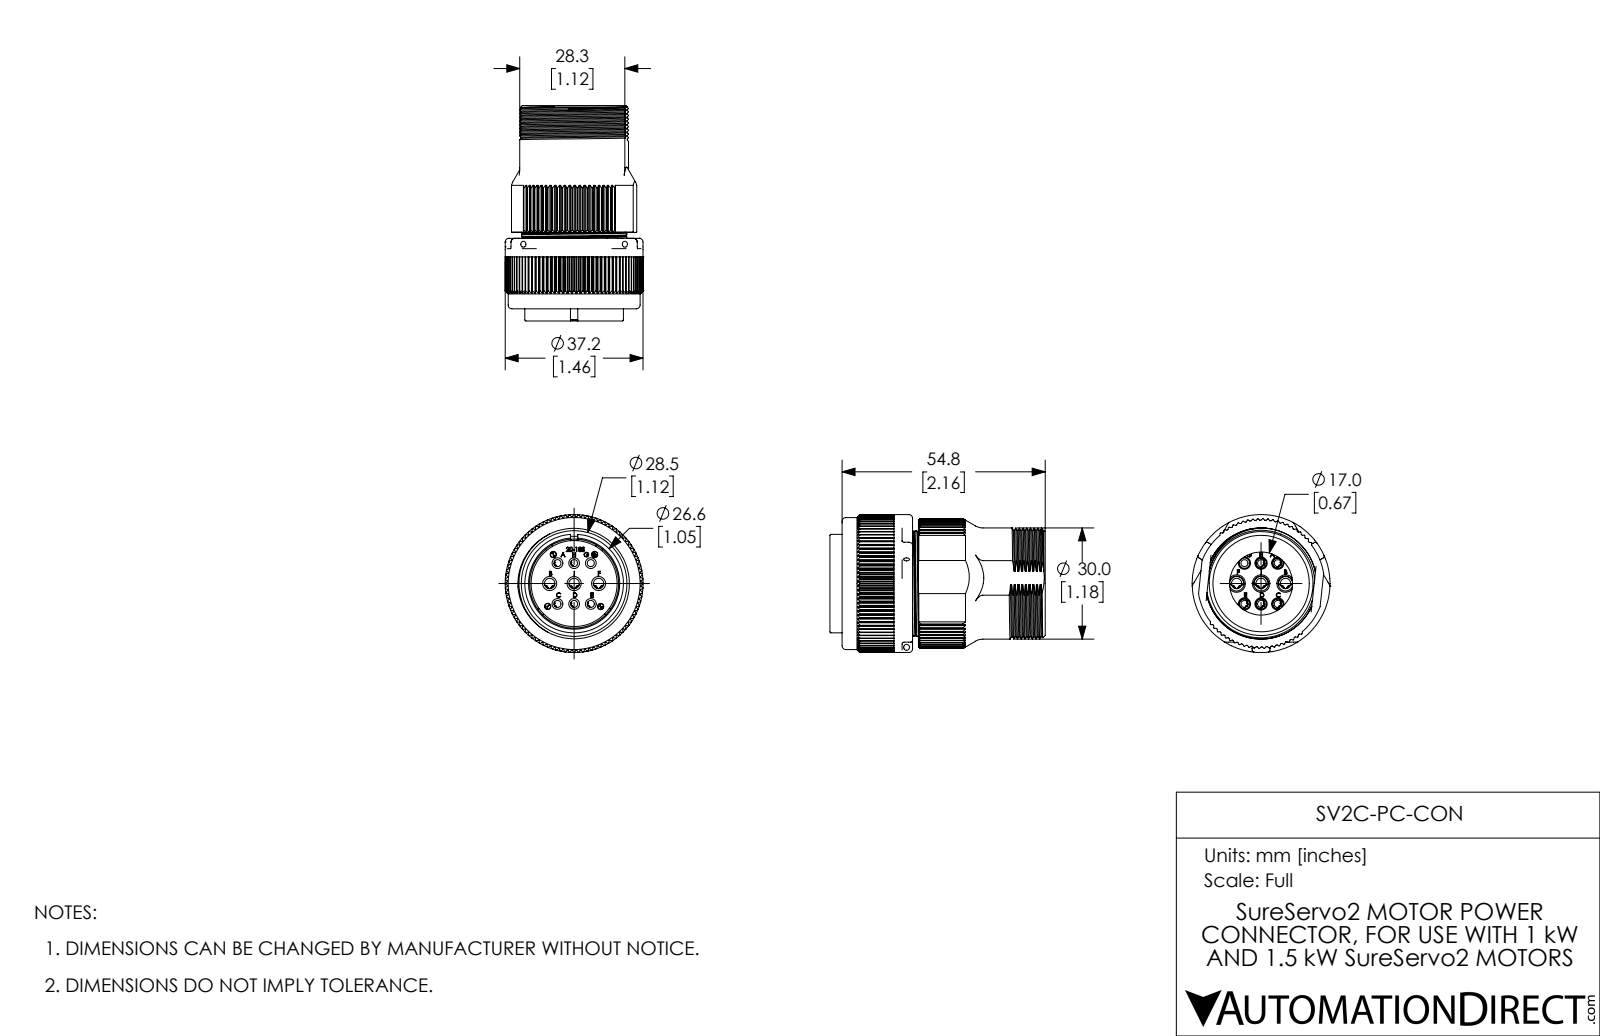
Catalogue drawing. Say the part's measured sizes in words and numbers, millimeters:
The part is named "SV2C-PC-CON". Its 3-D file was written by "SolidWorks 2017 (AUTOMOTIVE_DESIGN)". It is 16 solids with 1983 faces: 1079 planar, 575 cylindrical and 329 other. Overall it measures 58.1 by 37.2 by 37.2 millimeters. Its volume is 30 660 cubic millimeters and its surface area 28 690 square millimeters. Round holes: 9 of diameter 2.8, 9 of diameter 4, 8 of diameter 1.5, 6 of diameter 1.9, 6 of diameter 3.3, 3 of diameter 1.6, 3 of diameter 4.7, 3 of diameter 5.2, 3 of diameter 5.6, 1 of diameter 17, 1 of diameter 24, 1 of diameter 24.2. Round bosses or shafts: 8 of diameter 1.7, 1 of diameter 37.2, 1 of diameter 35.6, 1 of diameter 30, 1 of diameter 28.7, 1 of diameter 28.5, 1 of diameter 28.4, 1 of diameter 27.5. Partial cylindrical surfaces (rounded edges, fillets, slot ends): 38 of radius 0.5, 30 of radius 0.1, 30 of radius 0.3, 6 of radius 0.3, 6 of radius 0.4, 5 of radius 1.3, 5 of radius 1.5, 3 of radius 1.9. The main face-to-face distances are 1.6, 1.4, 3.4, 7, 3.2, 3.8, 4.8, 5.2, 2.2, 8.6. The hole center spacings are 4.5, 5.9, 7.1, 8.6, 11.9, 12.4, 11, 2.5.
